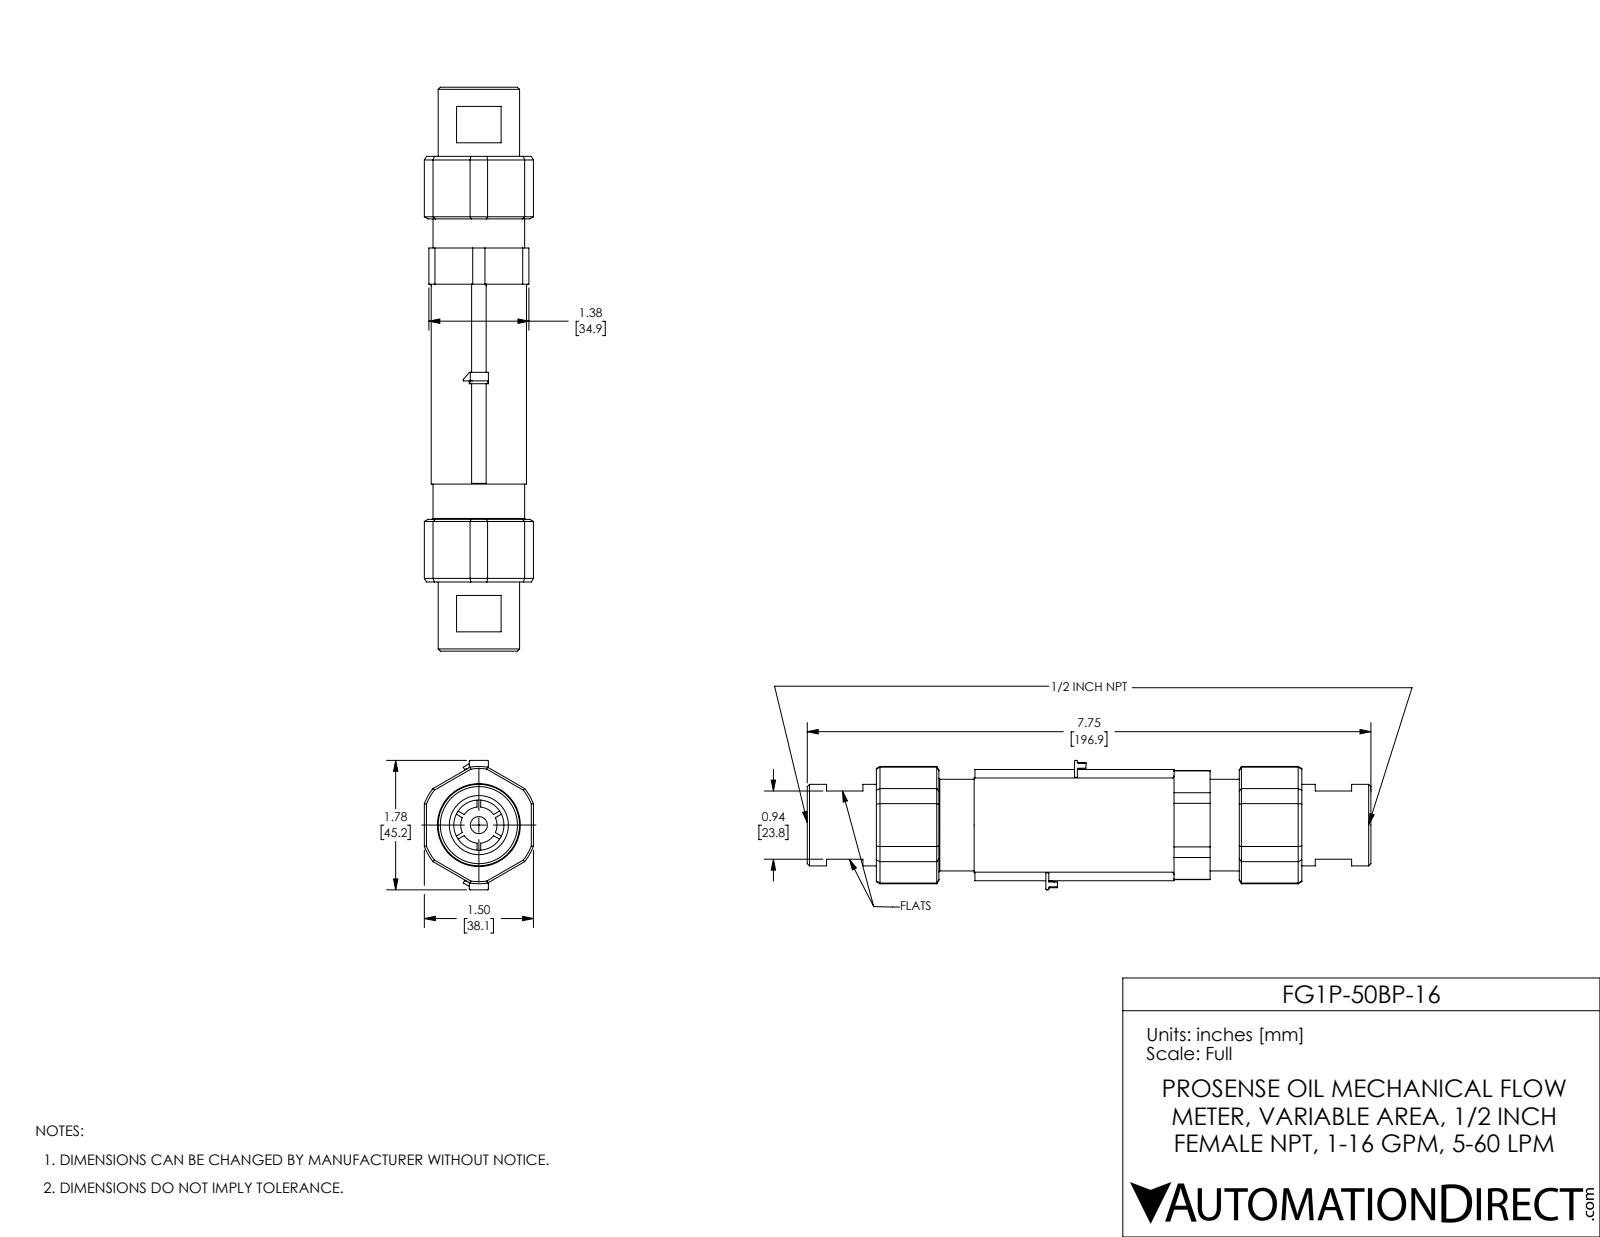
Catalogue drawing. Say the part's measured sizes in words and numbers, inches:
The part is named "FG1P-50BP-2". Its 3-D file was written by "SolidWorks 2017 (AUTOMOTIVE_DESIGN)". It is 5 solids with 404 faces: 148 planar, 163 cylindrical and 93 other. Overall it measures 7.75 by 1.78 by 1.5 inches. Its volume is 6.098 cubic inches and its surface area 93.75 square inches. Round holes: 1 of diameter 0.69, 1 of diameter 0.97, 1 of diameter 1.14, 1 of diameter 1.286. Round bosses or shafts: 1 of diameter 1.373, 1 of diameter 1.31, 1 of diameter 1.26, 1 of diameter 1.252, 1 of diameter 1.12, 1 of diameter 1.036, 1 of diameter 0.498. Partial cylindrical surfaces (rounded edges, fillets, slot ends): 12 of radius 0.012, 12 of radius 0.02, 4 of radius 0.005, 3 of radius 0.67, 3 of radius 0.75, 1 of radius 0.806. The main face-to-face distances are 1.5, 0.65, 0.85, 0.063, 1.437, 0.296, 1.234, 0.043, 0.09, 5.51.
